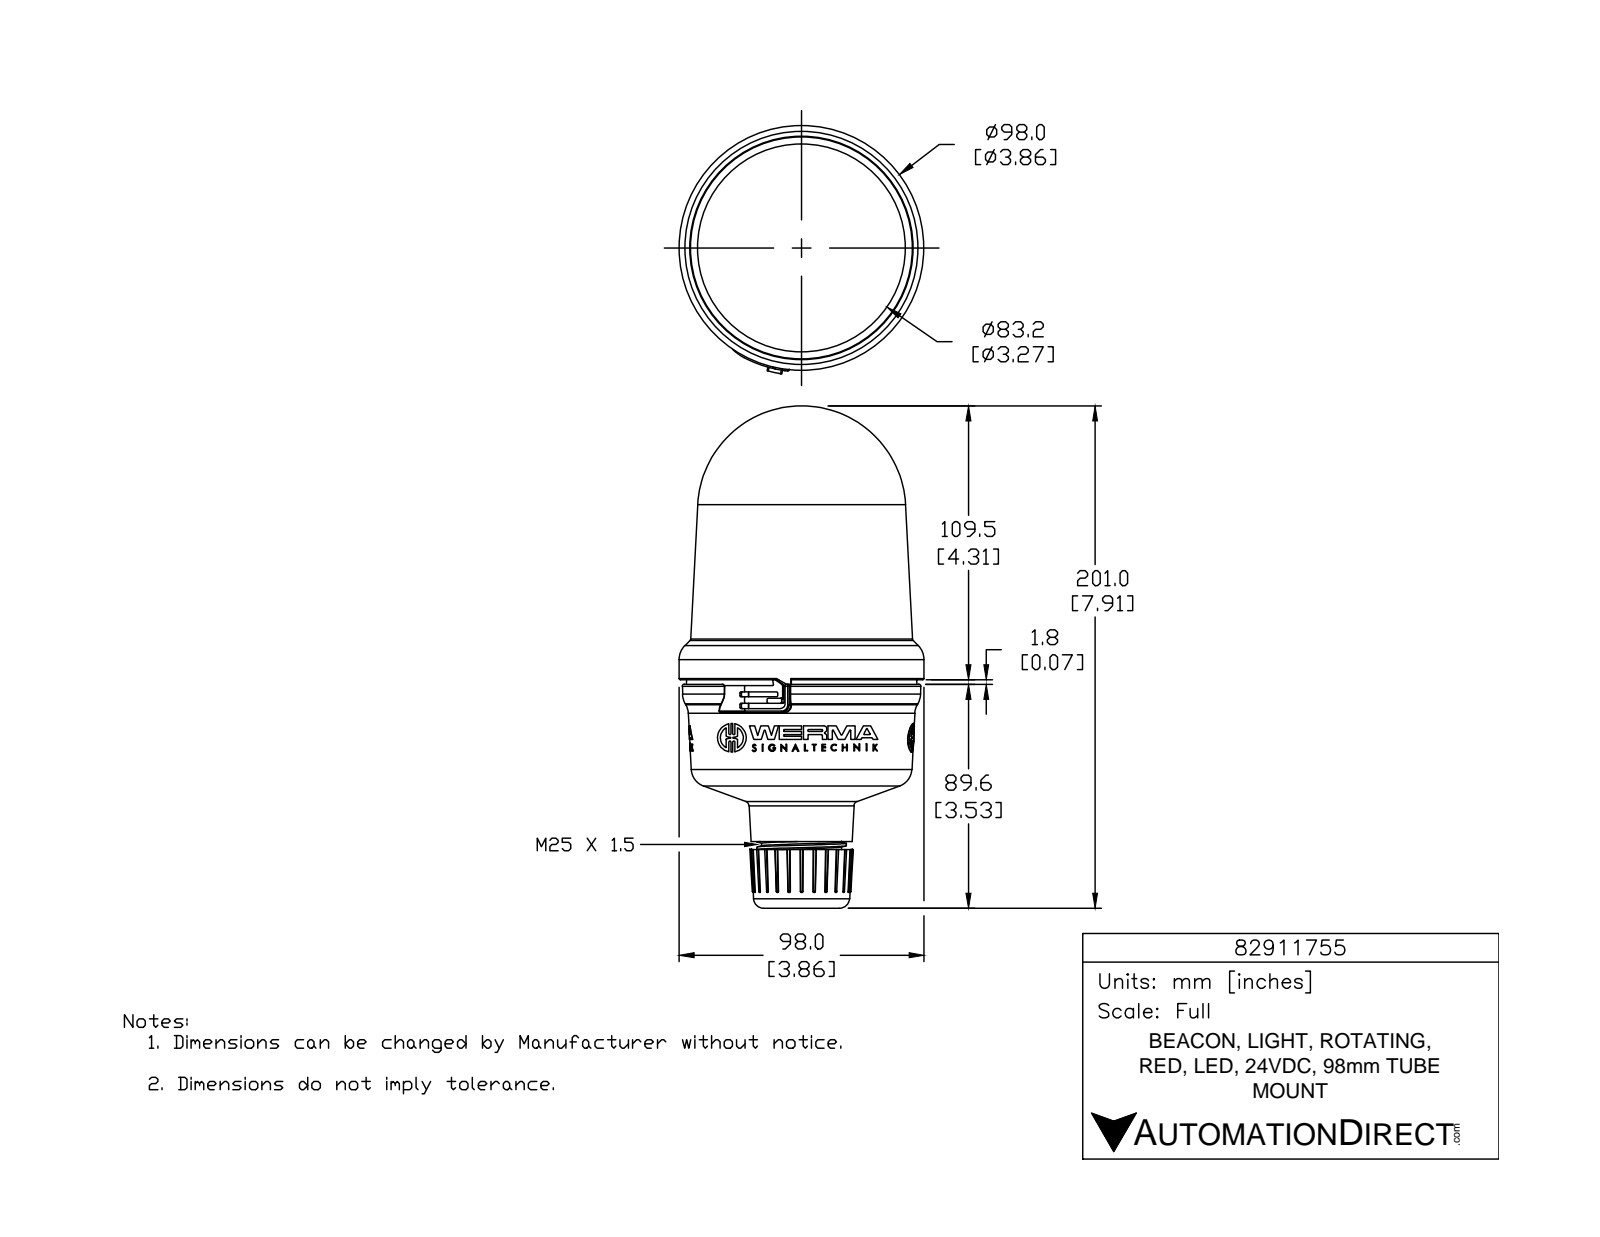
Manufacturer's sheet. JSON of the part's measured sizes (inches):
{"part_name": "82911755", "step_written_by": "SolidWorks 2015 (AUTOMOTIVE_DESIGN)", "units": "inches", "bodies": {"solids": 1, "faces": 1006, "planar": 554, "cylindrical": 189, "other": 263}, "overall_size": [7.914, 3.912, 3.858], "volume_in3": 54.7, "surface_area_in2": 91.39, "round_holes": [[0.078, 3], [1.013, 1], [1.024, 1]], "round_bosses_or_shafts": [[0.452, 3], [0.113, 3], [3.858, 1], [1.409, 1], [1.261, 1]], "partial_cylinders_radius": [[0.02, 12], [0.007, 9], [0.007, 6], [0.016, 6], [0.016, 6], [0.016, 6], [0.262, 6], [0.006, 3]], "face_to_face_distances": [2.214, 0.462, 2.676, 0.335, 0.127, 2.548, 2.603, 2.476, 2.141, 0.073]}
